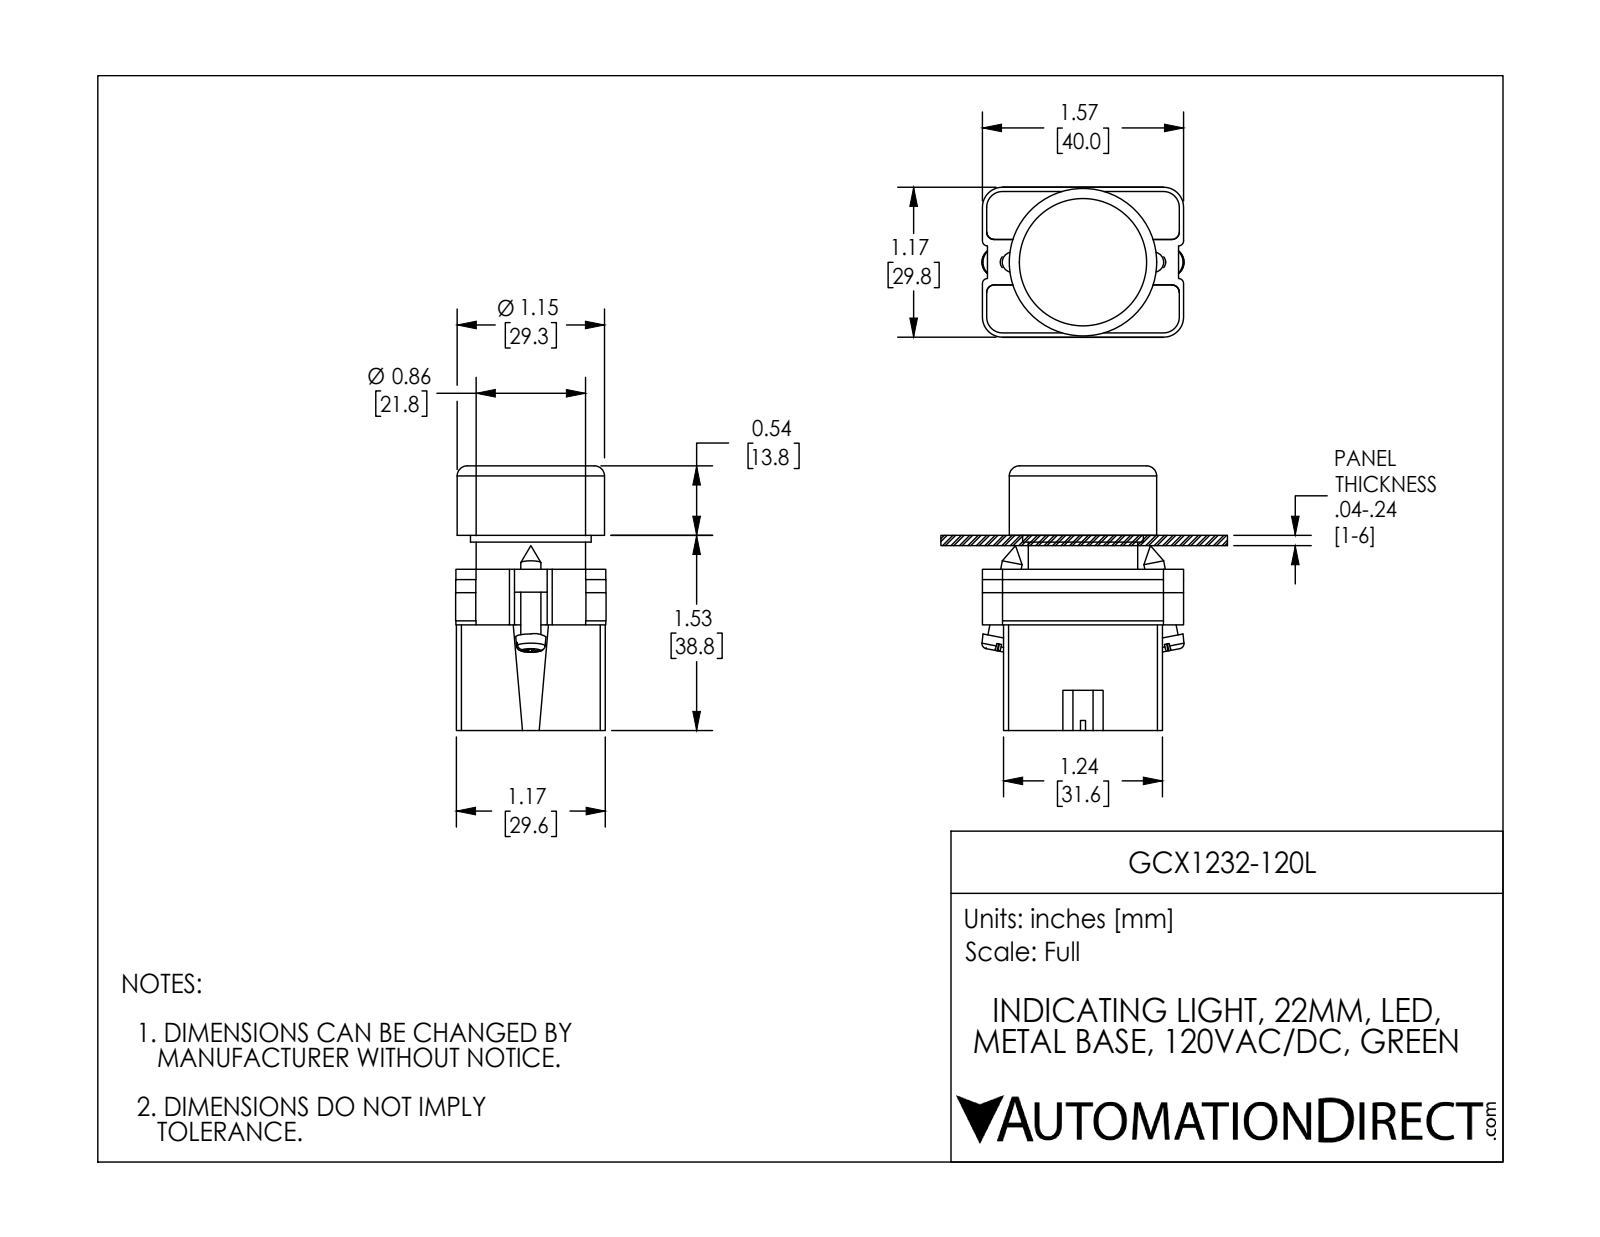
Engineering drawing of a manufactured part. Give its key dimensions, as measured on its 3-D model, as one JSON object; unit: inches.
{"part_name": "ecx1029; ECX1050; GCX1232-120L; GCX1232L OPERATOR", "step_written_by": "SolidWorks 2016 (AUTOMOTIVE_DESIGN)", "units": "inches", "bodies": {"solids": 7, "faces": 339, "planar": 178, "cylindrical": 134, "other": 27}, "overall_size": [2.071, 1.581, 1.177], "volume_in3": 2.268, "surface_area_in2": 31.19, "round_holes": [[0.124, 2], [0.13, 2], [0.197, 1], [0.469, 1], [0.852, 1], [0.878, 1], [0.888, 1], [1.102, 1]], "round_bosses_or_shafts": [[0.157, 4], [1.154, 1], [1.092, 1], [0.945, 1], [0.856, 1], [0.78, 1], [0.504, 1]], "partial_cylinders_radius": [[0.059, 24], [0.041, 12], [0.124, 12], [0.157, 12], [0.039, 8], [0.128, 2], [0.392, 1], [0.398, 1]], "face_to_face_distances": [0.86, 1.244, 0.827, 1.687, 1.136, 0.033, 1.963, 0.276, 0.031, 1.165]}
